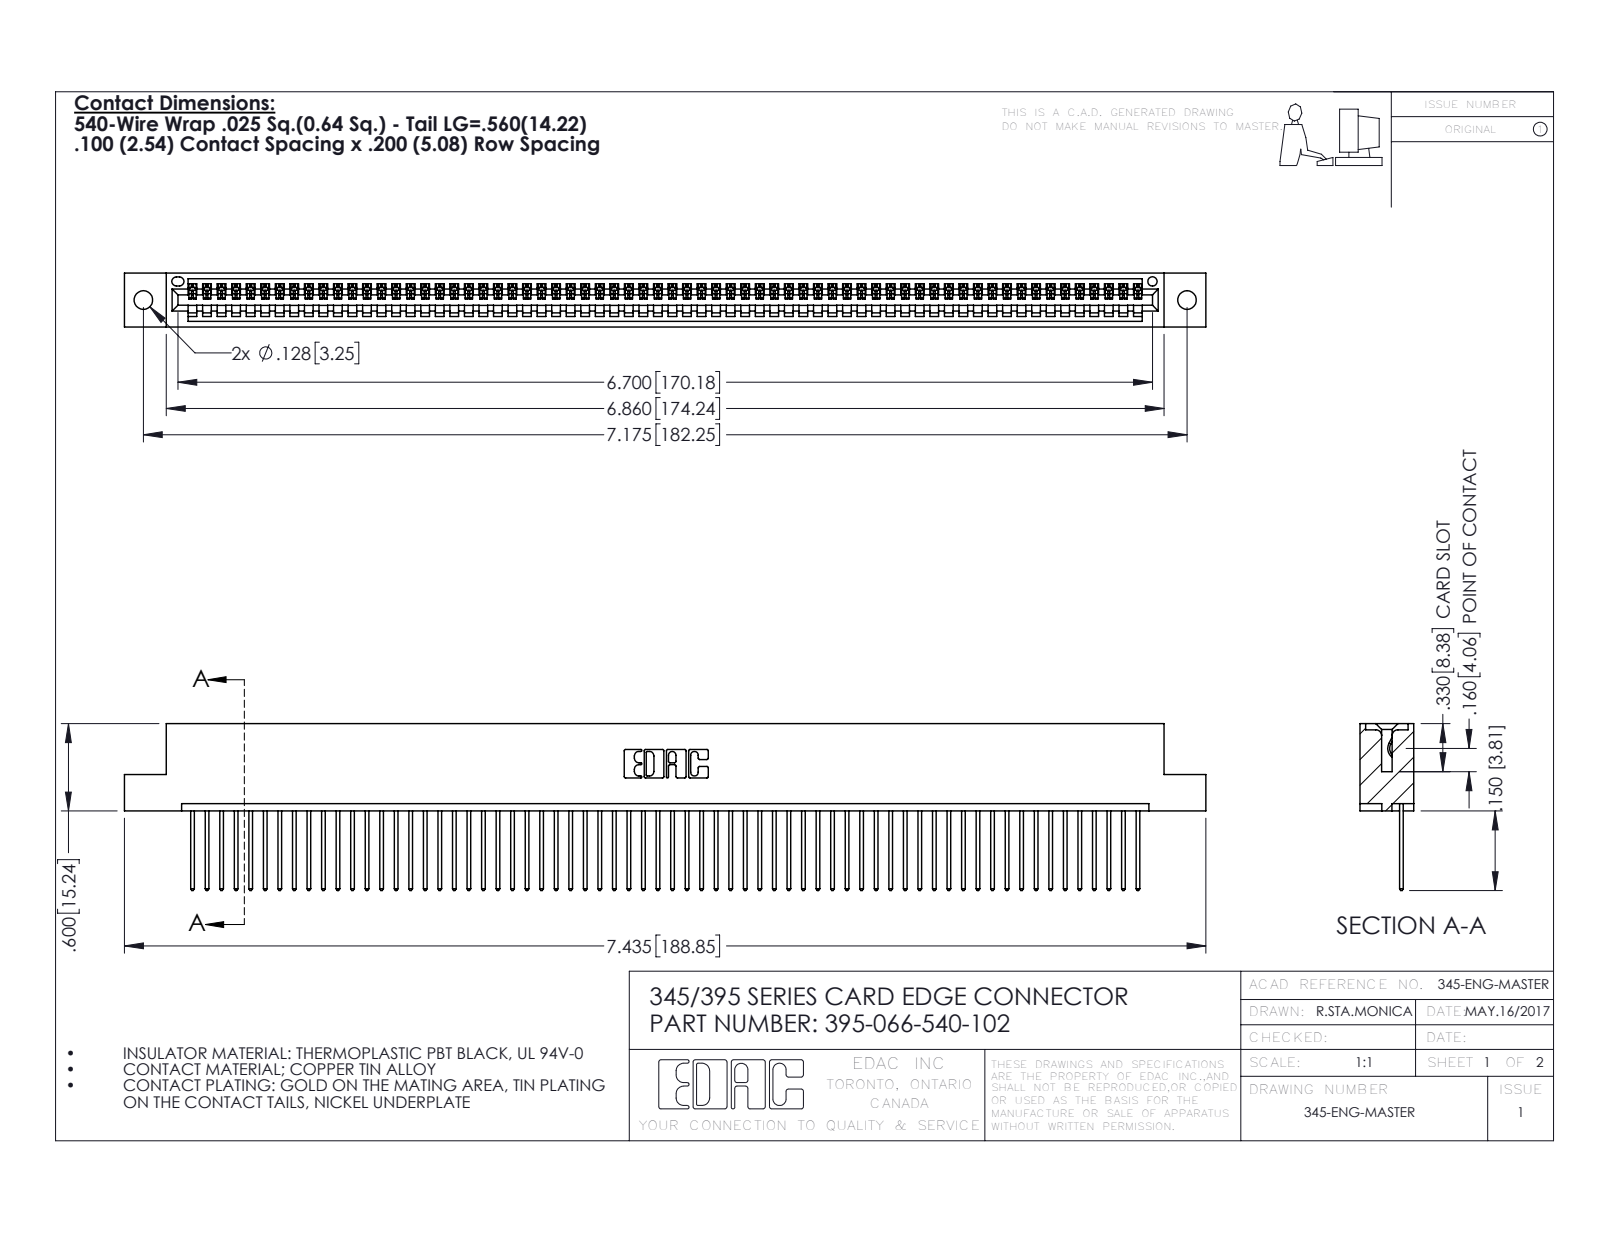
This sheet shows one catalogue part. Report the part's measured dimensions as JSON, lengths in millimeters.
{"part_name": "345 Part_Flush Mounting Lugs - 0.128 Dia; 345-292-001_345-293-140; 395-066-540-102", "step_written_by": "SolidWorks 2016 (CONFIG_CONTROL_DESIGN)", "units": "millimeters", "bodies": {"solids": 67, "faces": 3954, "planar": 2720, "cylindrical": 1234, "other": 0}, "overall_size": [188.8, 29.1, 9.4], "volume_mm3": 18190, "surface_area_mm2": 24860, "round_holes": [[3.3, 2], [1.6, 1]], "partial_cylinders_radius": [[0.2, 132], [0.3, 132], [0.3, 22], [0.2, 6], [0.8, 6], [0.7, 3], [0.8, 2], [1, 2]], "face_to_face_distances": [1.8, 7.6, 9.4, 2.5, 6.9, 0.6, 5.1, 5.7, 3.8, 1.8], "hole_center_spacings": [6.9, 176.3, 182.2]}
